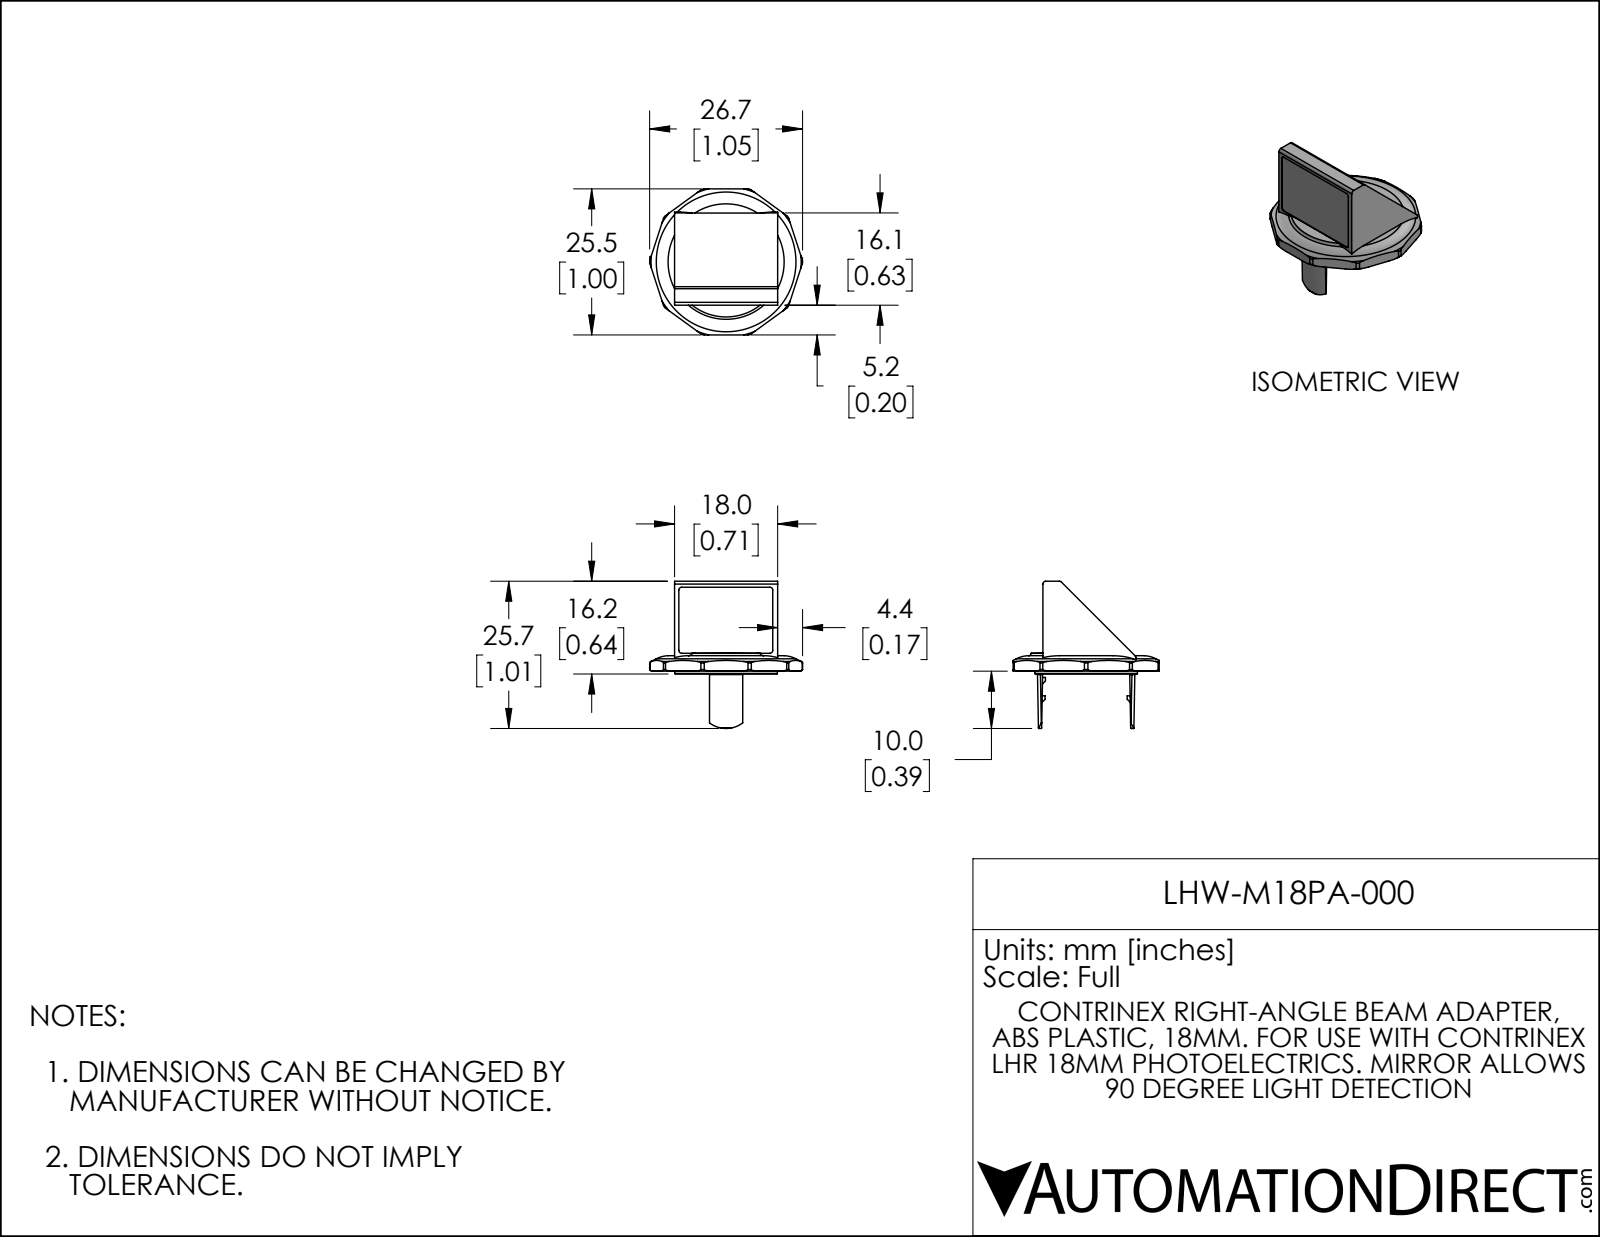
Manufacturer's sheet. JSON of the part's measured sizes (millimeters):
{"part_name": "LHW-M18PA-000", "step_written_by": "SolidWorks 2021 (AUTOMOTIVE_DESIGN)", "units": "millimeters", "bodies": {"solids": 1, "faces": 175, "planar": 101, "cylindrical": 32, "other": 42}, "overall_size": [26.7, 25.7, 25.5], "volume_mm3": 1600, "surface_area_mm2": 3023, "round_bosses_or_shafts": [[25, 1], [17.9, 1]], "partial_cylinders_radius": [[1, 10], [0.5, 7], [0.1, 2], [0.1, 2], [4.8, 1], [7.8, 1], [8.4, 1]], "face_to_face_distances": [0.6, 1.1, 16.9, 1, 18, 11.1, 6.9, 10.3, 0.8, 7.7]}
